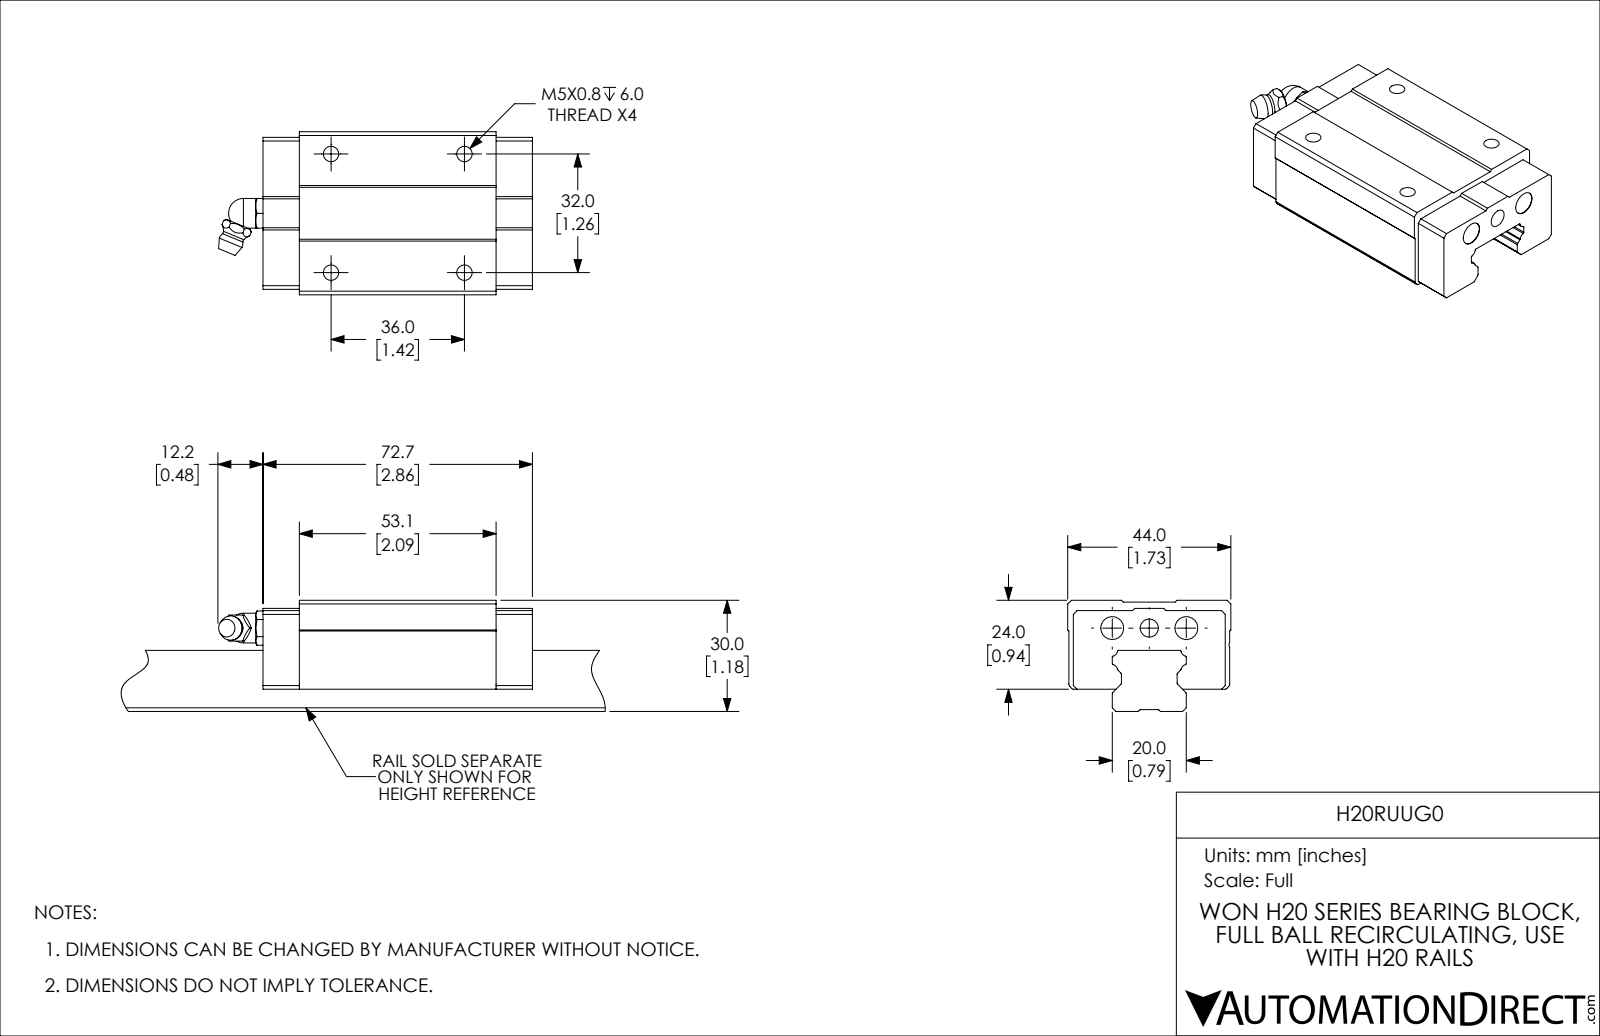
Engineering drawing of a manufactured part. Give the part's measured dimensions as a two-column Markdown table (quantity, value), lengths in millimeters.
| quantity | value |
| --- | --- |
| part name | H20RUUG0 |
| STEP written by | SolidWorks 2019 (CONFIG_CONTROL_DESIGN) |
| units | millimeters |
| bodies | 2 solids, 150 faces (75 planar, 45 cylindrical, 30 other) |
| overall size | 84.7 × 44 × 24 |
| volume | 59 262 mm³ |
| surface area | 14 097 mm² |
| round holes (diameter × count) | 4.13 × 4, 6.2 × 2, 4.92 × 1 |
| round bosses / shafts (diameter × count) | 8 × 1, 6 × 1 |
| partial cylindrical surfaces (radius × count) | 0.5 × 8, 1 × 5, 0.3 × 4, 1.6 × 4 |
| main face-to-face distances | 10.5, 24, 13.5, 13, 1.2, 42.2, 23.5, 0.5, 1.5, 42.5 |
| hole center spacings | 10, 32, 36, 48.17, 20 |
